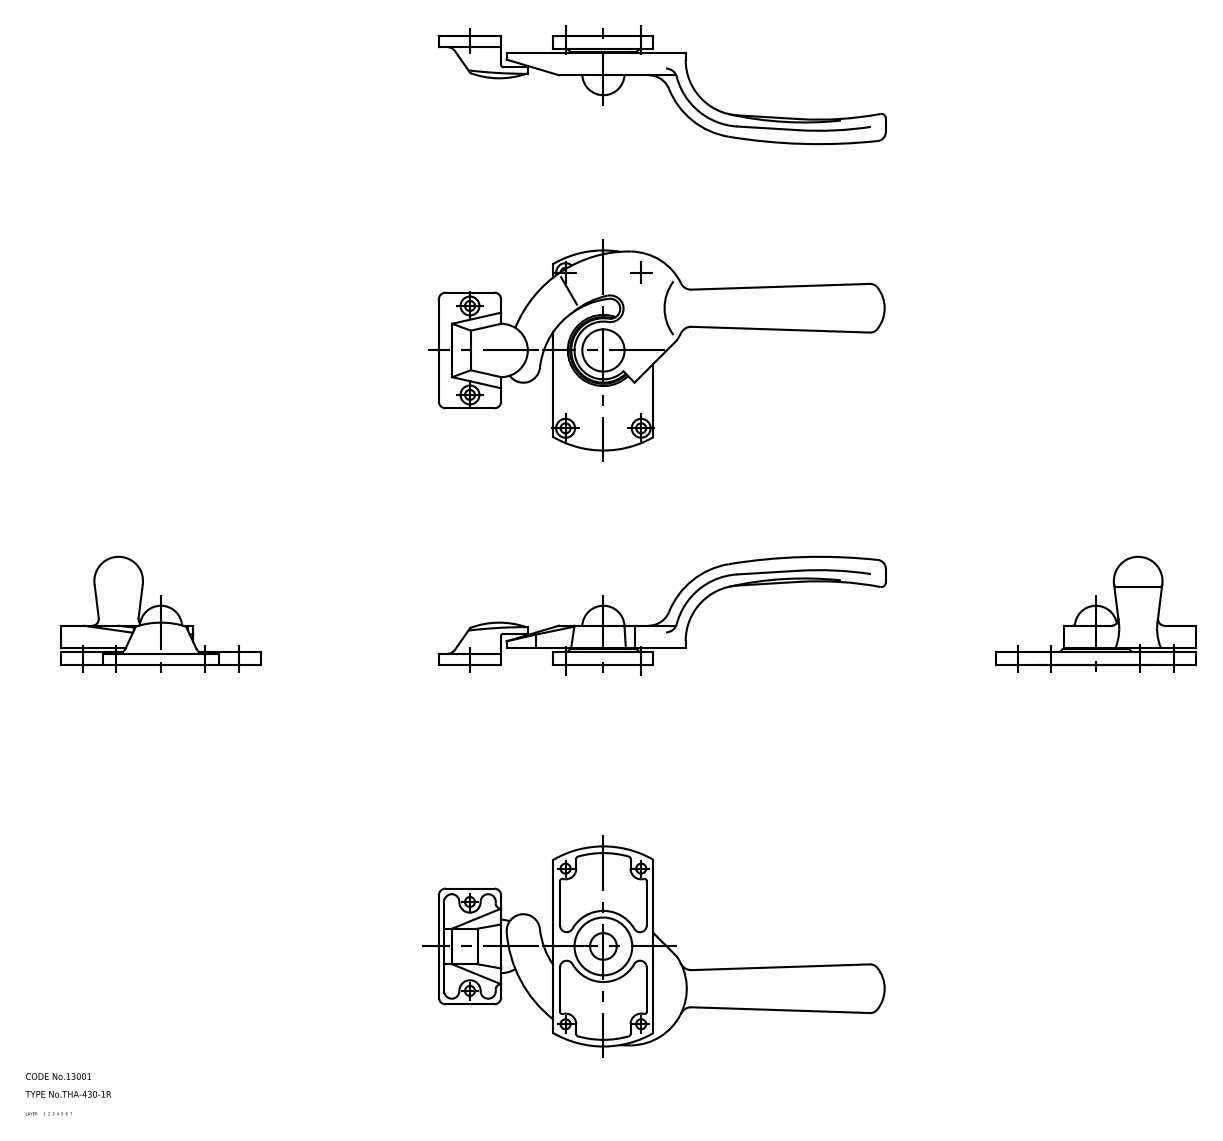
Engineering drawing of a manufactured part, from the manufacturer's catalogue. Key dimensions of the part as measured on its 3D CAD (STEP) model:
Part name (STEP PRODUCT): washer_C_mr; washer_B_mr; rivet_mr; keeper_mr (+3 more)
STEP written by: CADfix (AUTOMOTIVE_DESIGN)
Units: millimetres
Bodies: 6 solids, 173 faces (0 planar, 0 cylindrical, 173 other)
Overall size (bounding box): 201 × 90 × 48.59
Volume: 72 960 mm³ · Surface area: 32 857 mm²
